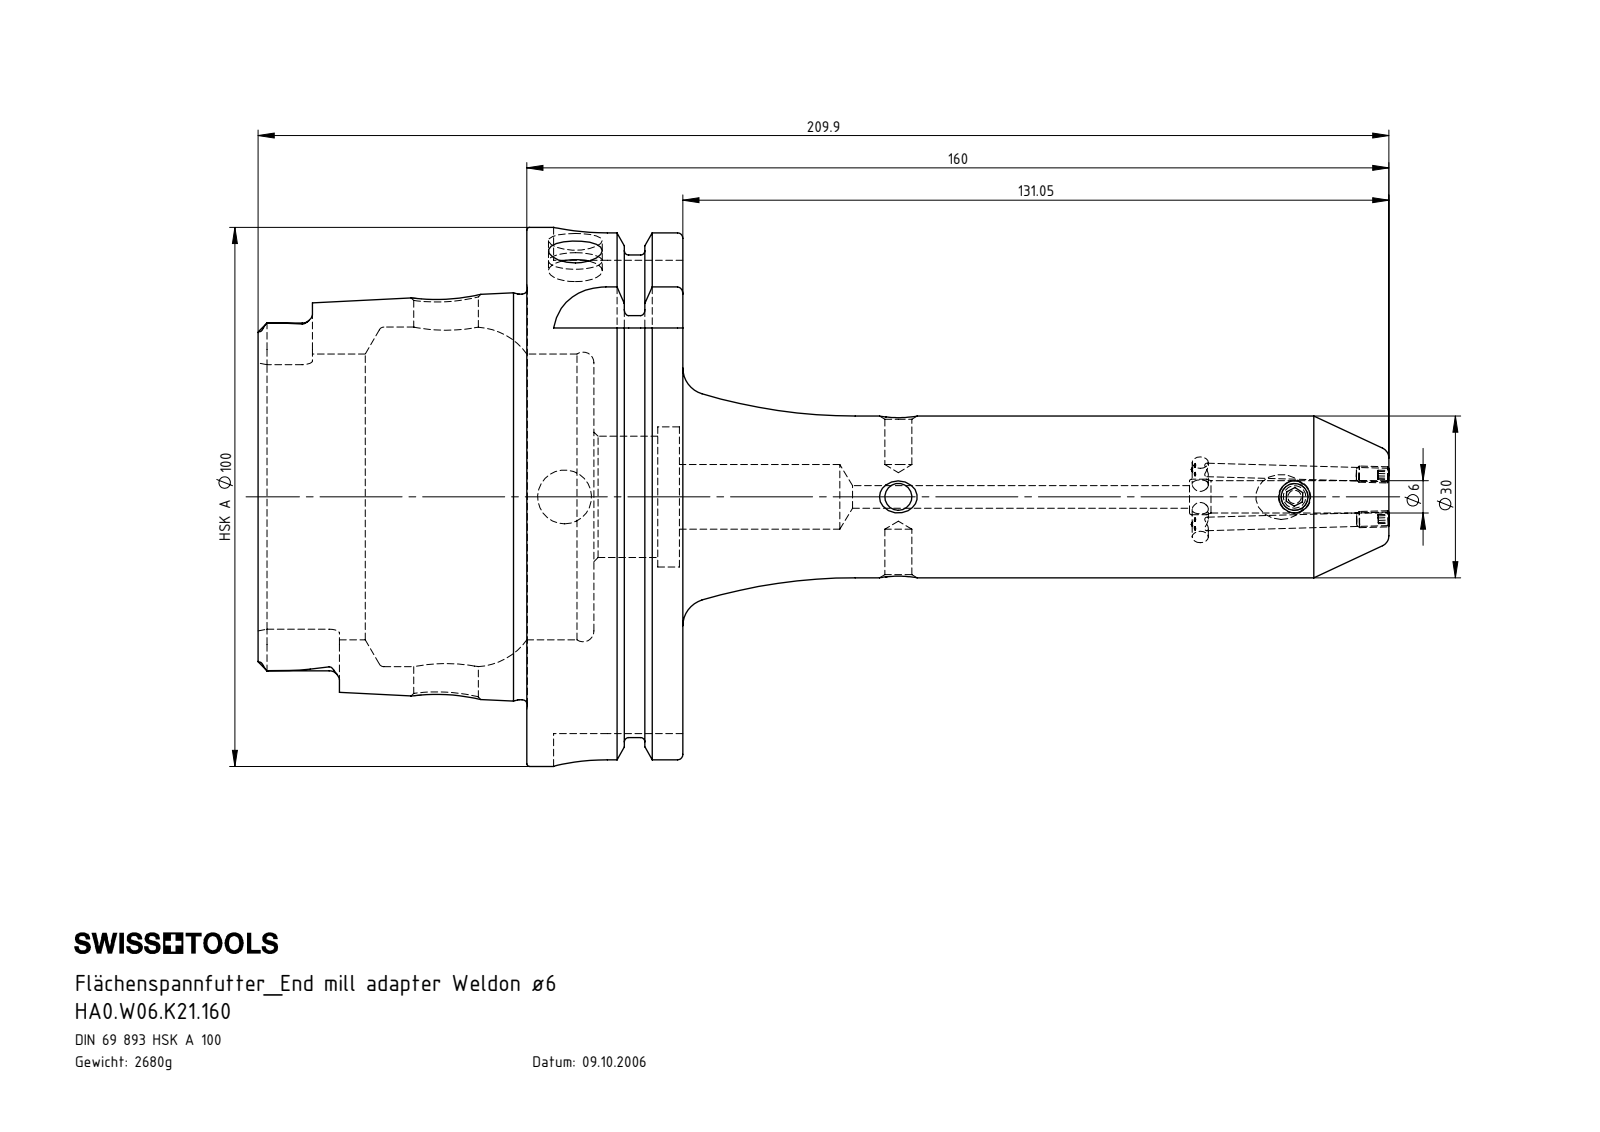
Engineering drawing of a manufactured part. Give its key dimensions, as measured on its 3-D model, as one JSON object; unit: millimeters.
{"part_name": "HA0.W06.K21.160; W06-ER1.001.010; ERU-CJ2.001.006; HA0-W06.K21.160_C_Fertigbearbeitung", "step_written_by": "SolidWorks 2012 (CONFIG_CONTROL_DESIGN)", "units": "millimeters", "bodies": {"solids": 4, "faces": 277, "planar": 71, "cylindrical": 84, "other": 122}, "overall_size": [209.98, 100, 100], "volume_mm3": 341348, "surface_area_mm2": 65683, "round_holes": [[5, 3], [10, 3], [2.5, 2], [12, 2], [3, 1], [4.2, 1], [6, 1], [6.6, 1], [22.5, 1], [26, 1], [53, 1], [63, 1]], "round_bosses_or_shafts": [[3, 2], [100, 1], [91.95, 1], [75.26, 1], [30, 1], [6, 1]], "partial_cylinders_radius": [[1.9, 6], [4.88, 4], [10, 4]], "face_to_face_distances": [28.95, 12.45, 16.5, 49.9, 62.35, 78.85, 87.8, 78.2, 28.3, 15.85], "hole_center_spacings": [61.95, 73.55, 83.95, 135.5]}
